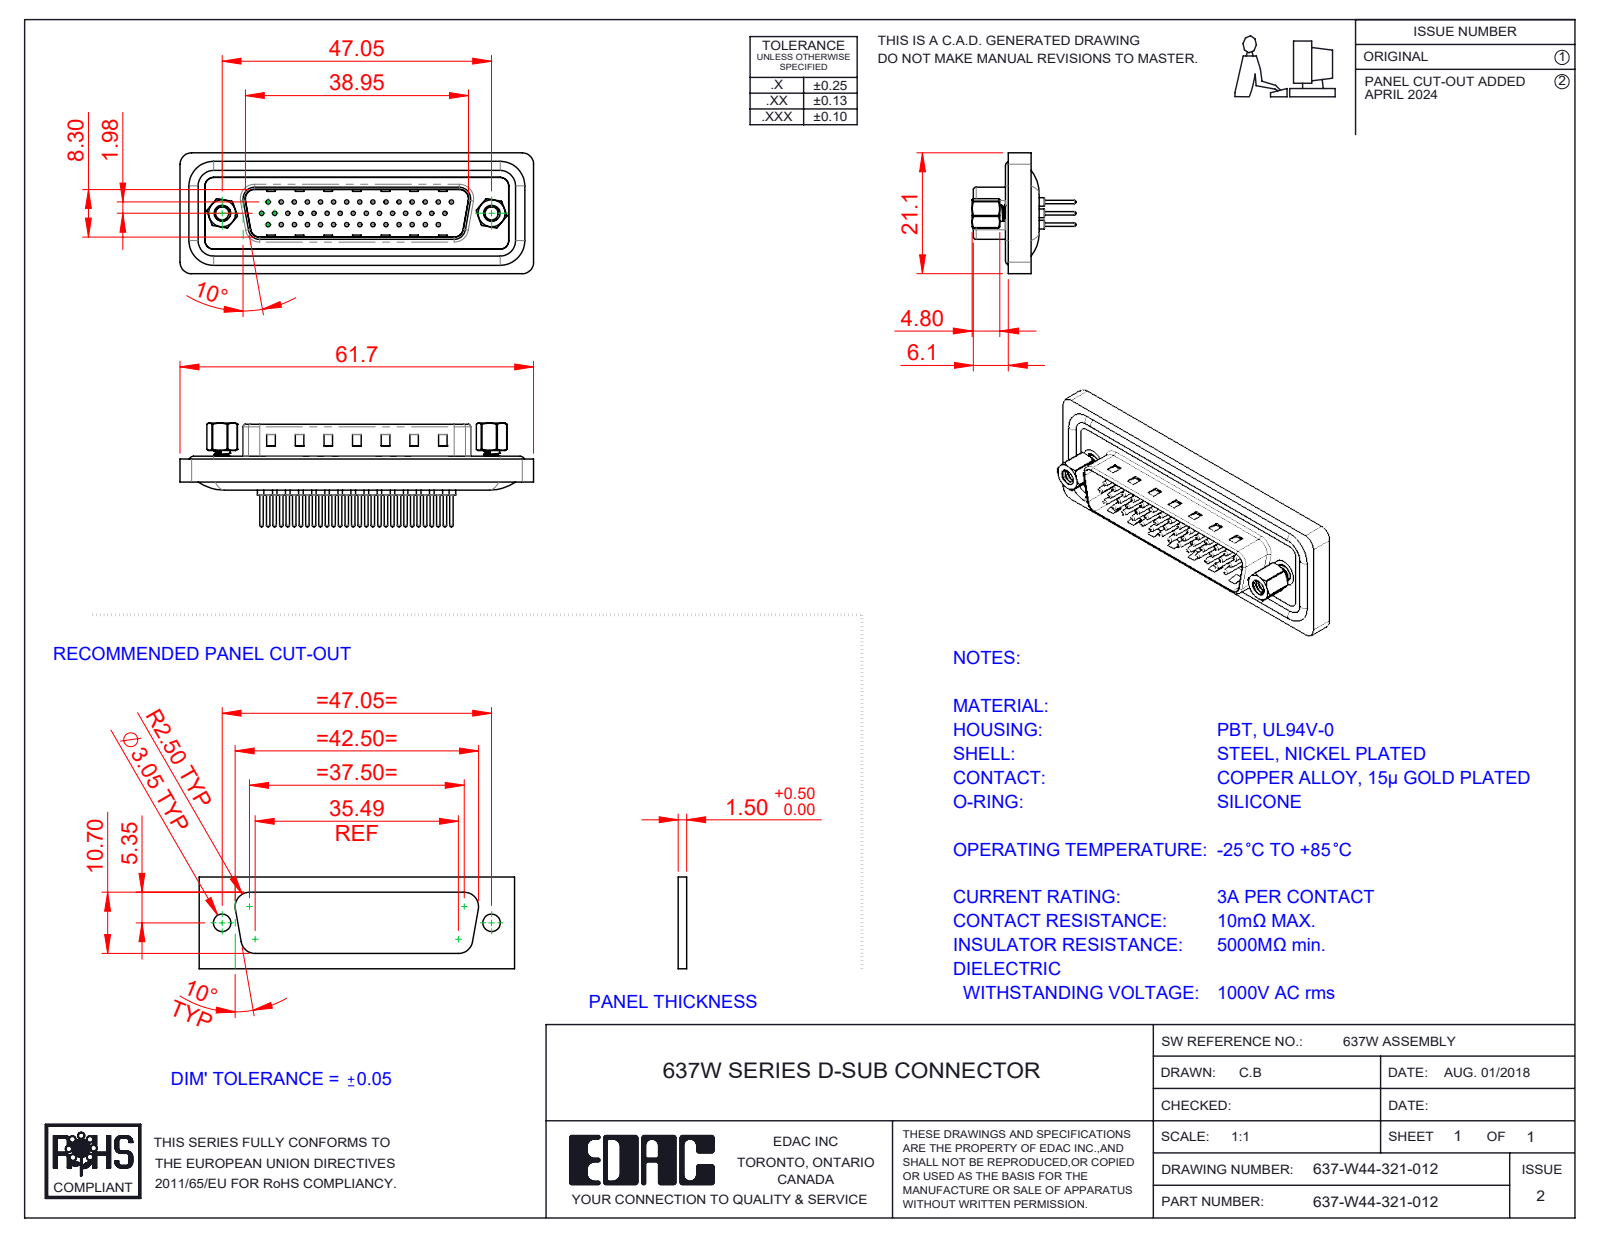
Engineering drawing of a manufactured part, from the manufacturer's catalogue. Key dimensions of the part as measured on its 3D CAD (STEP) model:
Part name (STEP PRODUCT): 637W Shell_44 Contacts; 637W Housing_44 Contacts; 637-W44-321-012; 637W 4-40 Hex Standoff (+5 more)
STEP written by: SolidWorks 2016 (CONFIG_CONTROL_DESIGN)
Units: millimetres
Bodies: 52 solids, 2234 faces (513 planar, 920 cylindrical, 801 other)
Overall size (bounding box): 61.74 × 21.1 × 17.9
Volume: 6 372 mm³ · Surface area: 12 028 mm²
Round holes (diameter × count): ⌀0.75 ×44, ⌀1.5 ×44, ⌀1.6 ×44, ⌀2 ×44, ⌀2.26 ×2, ⌀2.29 ×2, ⌀4 ×2, ⌀4.8 ×2, ⌀5 ×2
Round bosses / shafts (diameter × count): ⌀0.6 ×44, ⌀1.5 ×21, ⌀1.6 ×4, ⌀4.9 ×2, ⌀2.79 ×2, ⌀5 ×1
Partial cylindrical surfaces — rounded edges, fillets, slot ends (radius × count): R2 ×14, R1.5 ×13, R0.5 ×8, R2.7 ×6, R0.9 ×4, R1.6 ×4, R4.3 ×4, R0.4 ×2
Main face-to-face distances: 0.4, 1.6, 2.5, 2.9, 1.1, 5.65, 15.45, 0.75, 6.4, 14.7
Hole centre spacings: 2.28, 3.96, 2.29, 4.57, 8.24, 6.86, 11.43, 14.99
